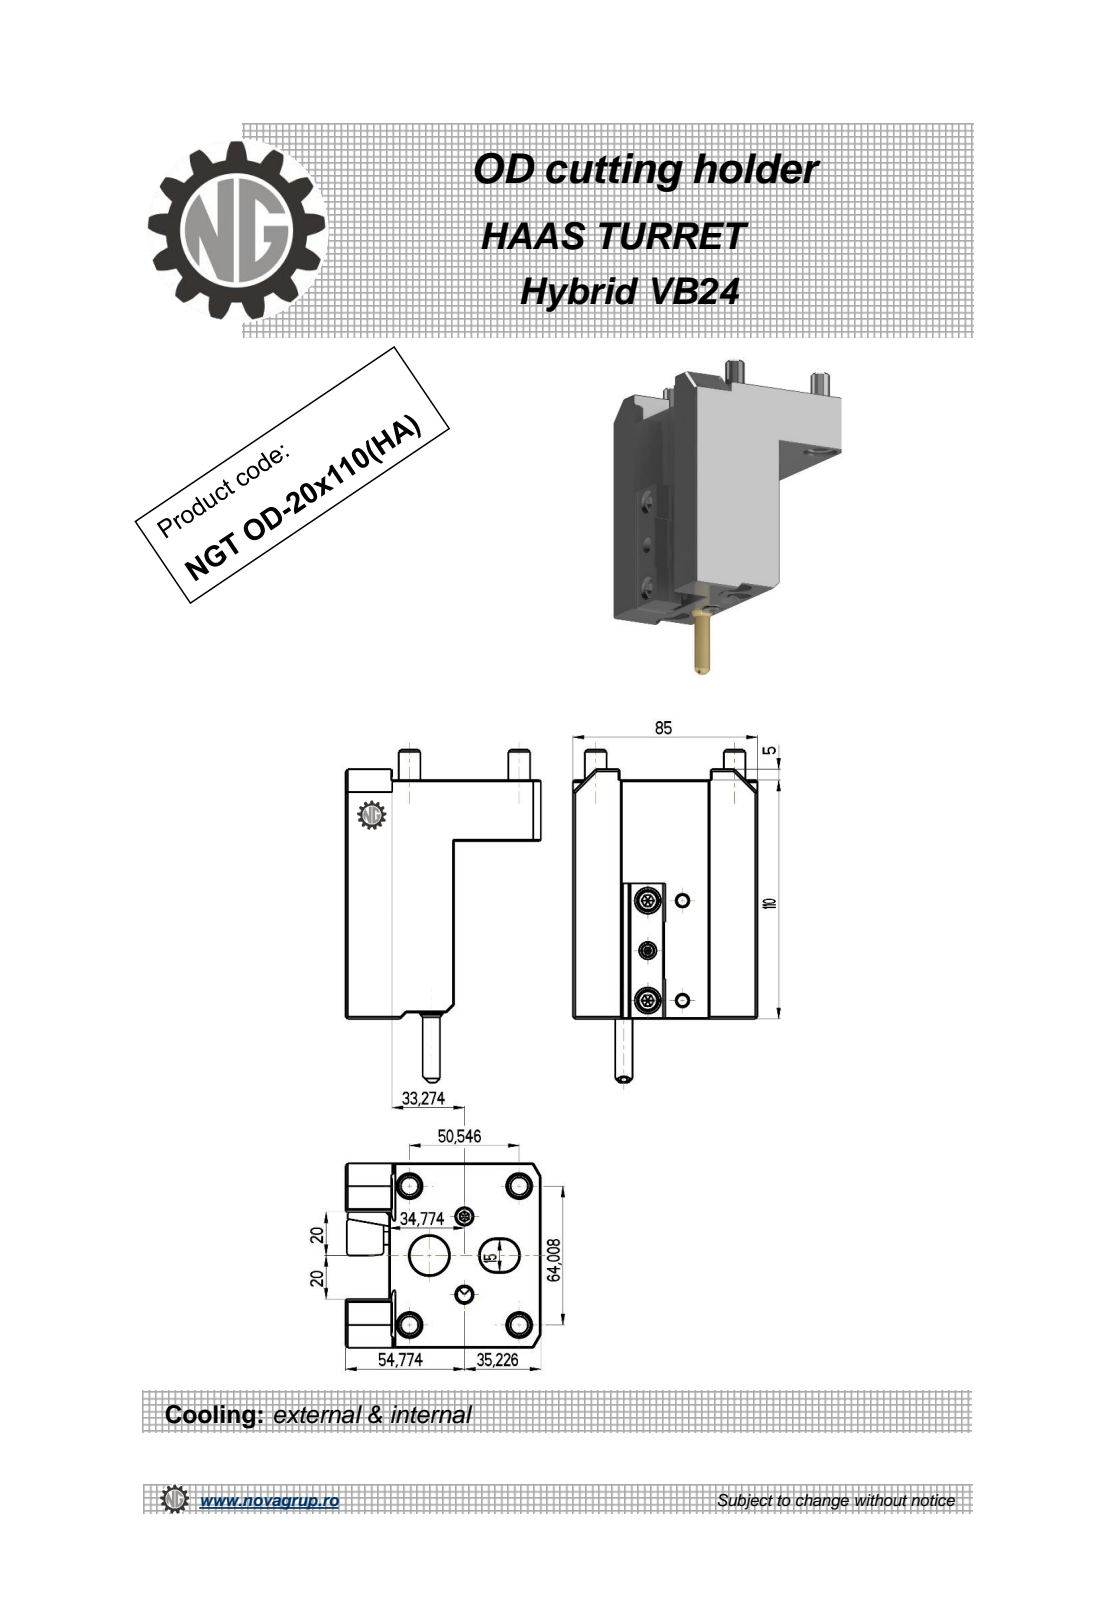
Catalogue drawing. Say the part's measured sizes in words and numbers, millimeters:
The part is named "NGT_OD_20_110_HA". Its 3-D file was written by "PRO/ENGINEER BY PARAMETRIC TECHNOLOGY CORPORATION, 2010280 (CONFIG_CONTROL_DESIGN)". It is 1 solid with 208 faces: 130 planar, 41 cylindrical and 37 other. Overall it measures 153.34 by 90 by 85 millimeters. Its volume is 493 668 cubic millimeters and its surface area 55 950 square millimeters. Round holes: 1 of diameter 3, 1 of diameter 5, 1 of diameter 6.8, 1 of diameter 18. Round bosses or shafts: 5 of diameter 10, 3 of diameter 6, 1 of diameter 8. Partial cylindrical surfaces (rounded edges, fillets, slot ends): 6 of radius 0.2, 6 of radius 0.41, 2 of radius 7.5, 1 of radius 1. The main face-to-face distances are 85, 50, 20, 30, 62.5, 28, 22.5, 40, 90, 70. The hole center spacings are 19.02, 24.2, 40.03.
